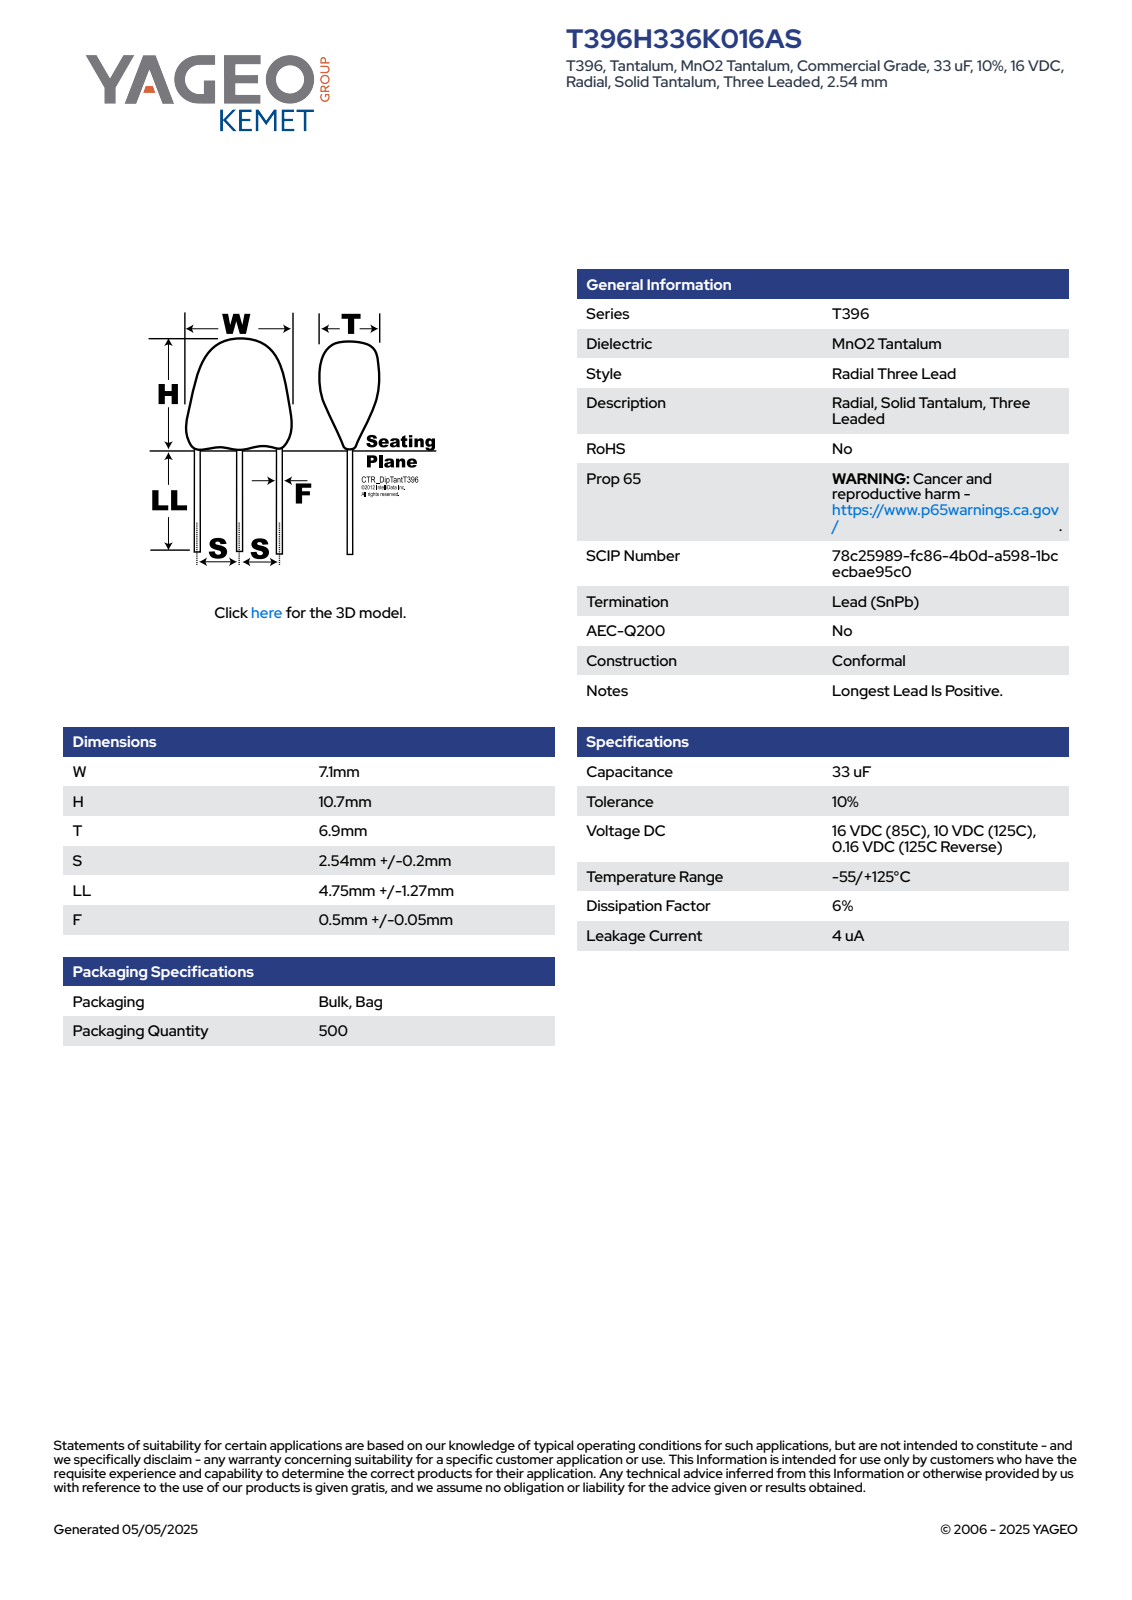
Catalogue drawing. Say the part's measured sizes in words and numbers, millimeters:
The part is named "CTR_T396_W7.1H10.7T6.9S2.54LL6.02F0.55". Its 3-D file was written by "SolidWorks 2014 (AUTOMOTIVE_DESIGN)". It is 4 solids with 88 faces: 70 planar, 8 cylindrical and 10 other. Overall it measures 16.72 by 7.1 by 4.8 millimeters. Its volume is 310 cubic millimeters and its surface area 290 square millimeters. Round bosses or shafts: 3 of diameter 0.55. Partial cylindrical surfaces (rounded edges, fillets, slot ends): 2 of radius 5. The main face-to-face distances are 4.8, 7.1, 6.02, 11.59, 5.57, 10.69, 4.67, 0.9, 0.73, 0.39.
